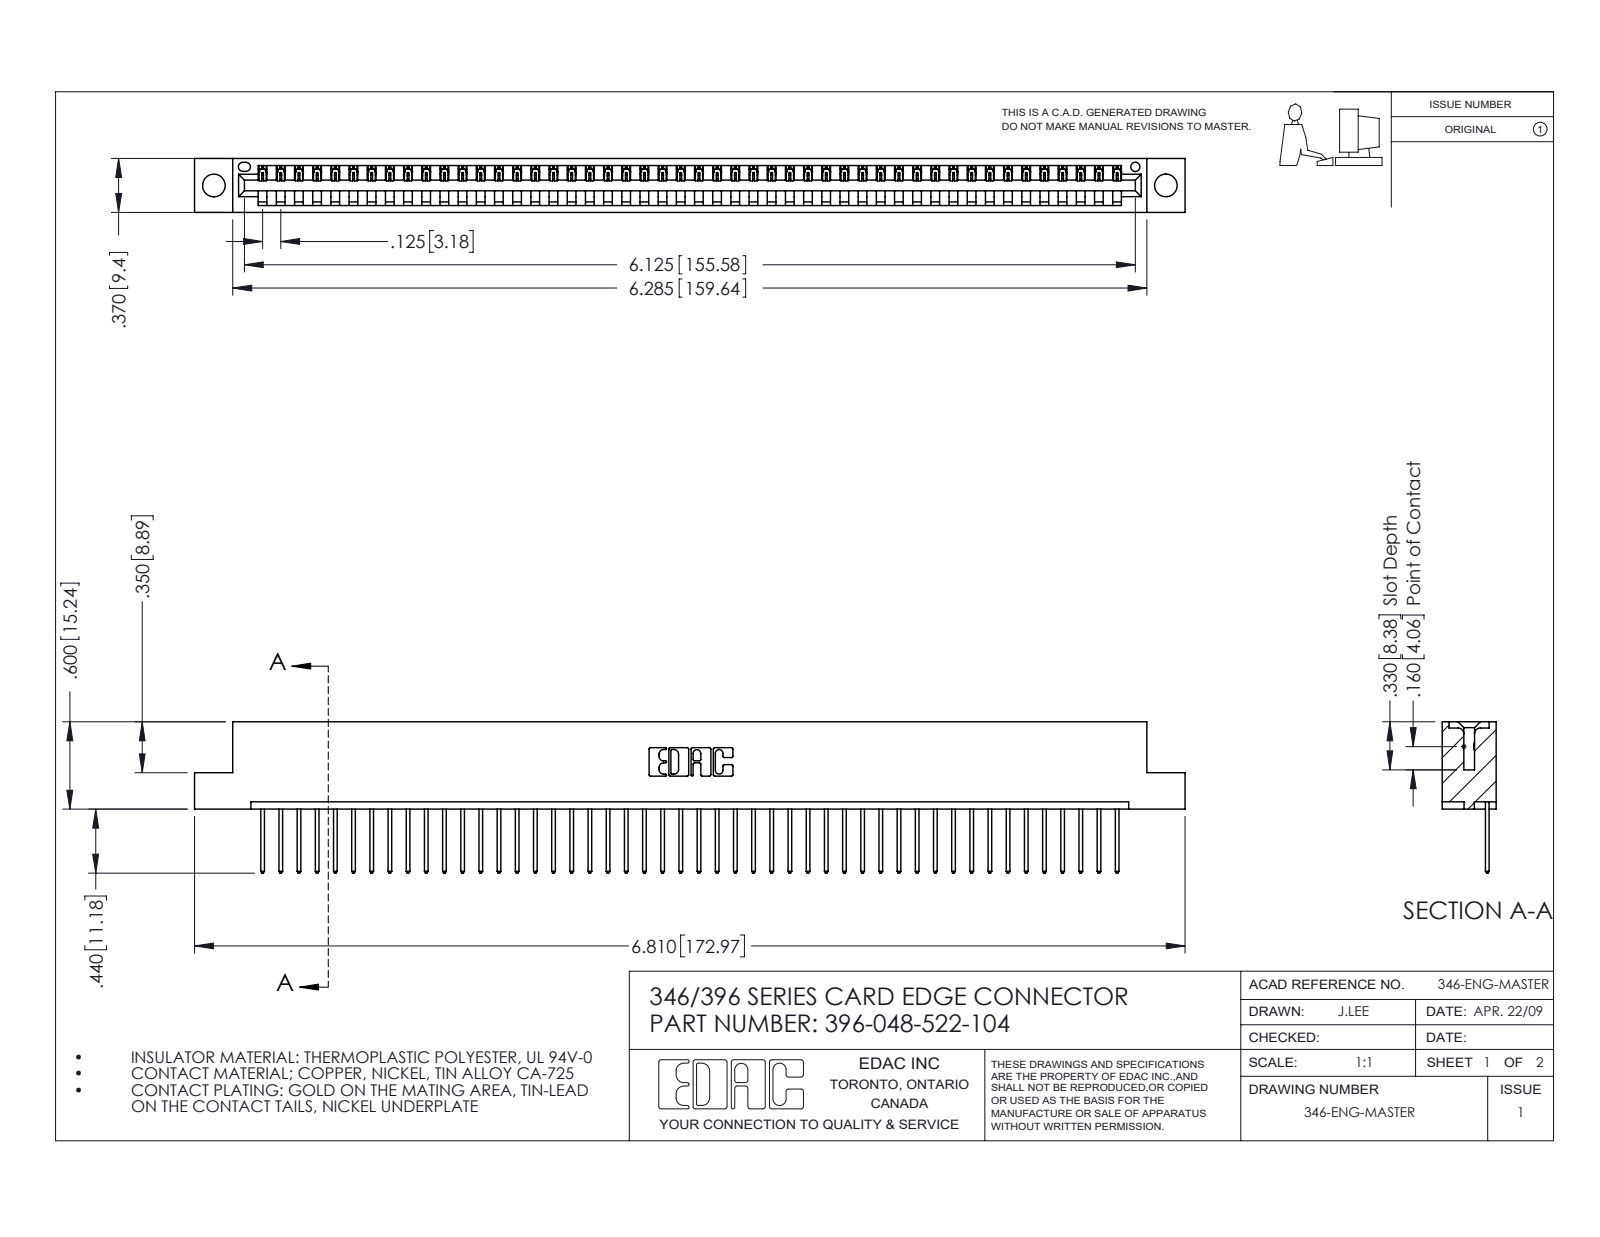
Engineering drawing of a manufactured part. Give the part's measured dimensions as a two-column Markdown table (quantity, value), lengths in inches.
| quantity | value |
| --- | --- |
| part name | 345-292-001_345-293-122; 346 Part_Flush Mounting Lugs - 0.156 Dia-TH; 396-048-522-104 |
| STEP written by | SolidWorks 2016 (CONFIG_CONTROL_DESIGN) |
| units | inches |
| bodies | 49 solids, 2906 faces (1996 planar, 910 cylindrical, 0 other) |
| overall size | 6.81 × 1.04 × 0.37 |
| volume | 1.008 in³ |
| surface area | 32.07 in² |
| round holes (diameter × count) | 0.156 × 2, 0.064 × 1 |
| partial cylindrical surfaces (radius × count) | 0.006 × 96, 0.01 × 96, 0.01 × 22, 0.007 × 6, 0.031 × 6, 0.026 × 3, 0.031 × 2, 0.04 × 2 |
| main face-to-face distances | 0.048, 0.322, 0.37, 0.25, 0.072, 0.298, 0.025, 0.148, 0.222, 0.1 |
| hole center spacings | 0.246, 6.336, 6.545 |
